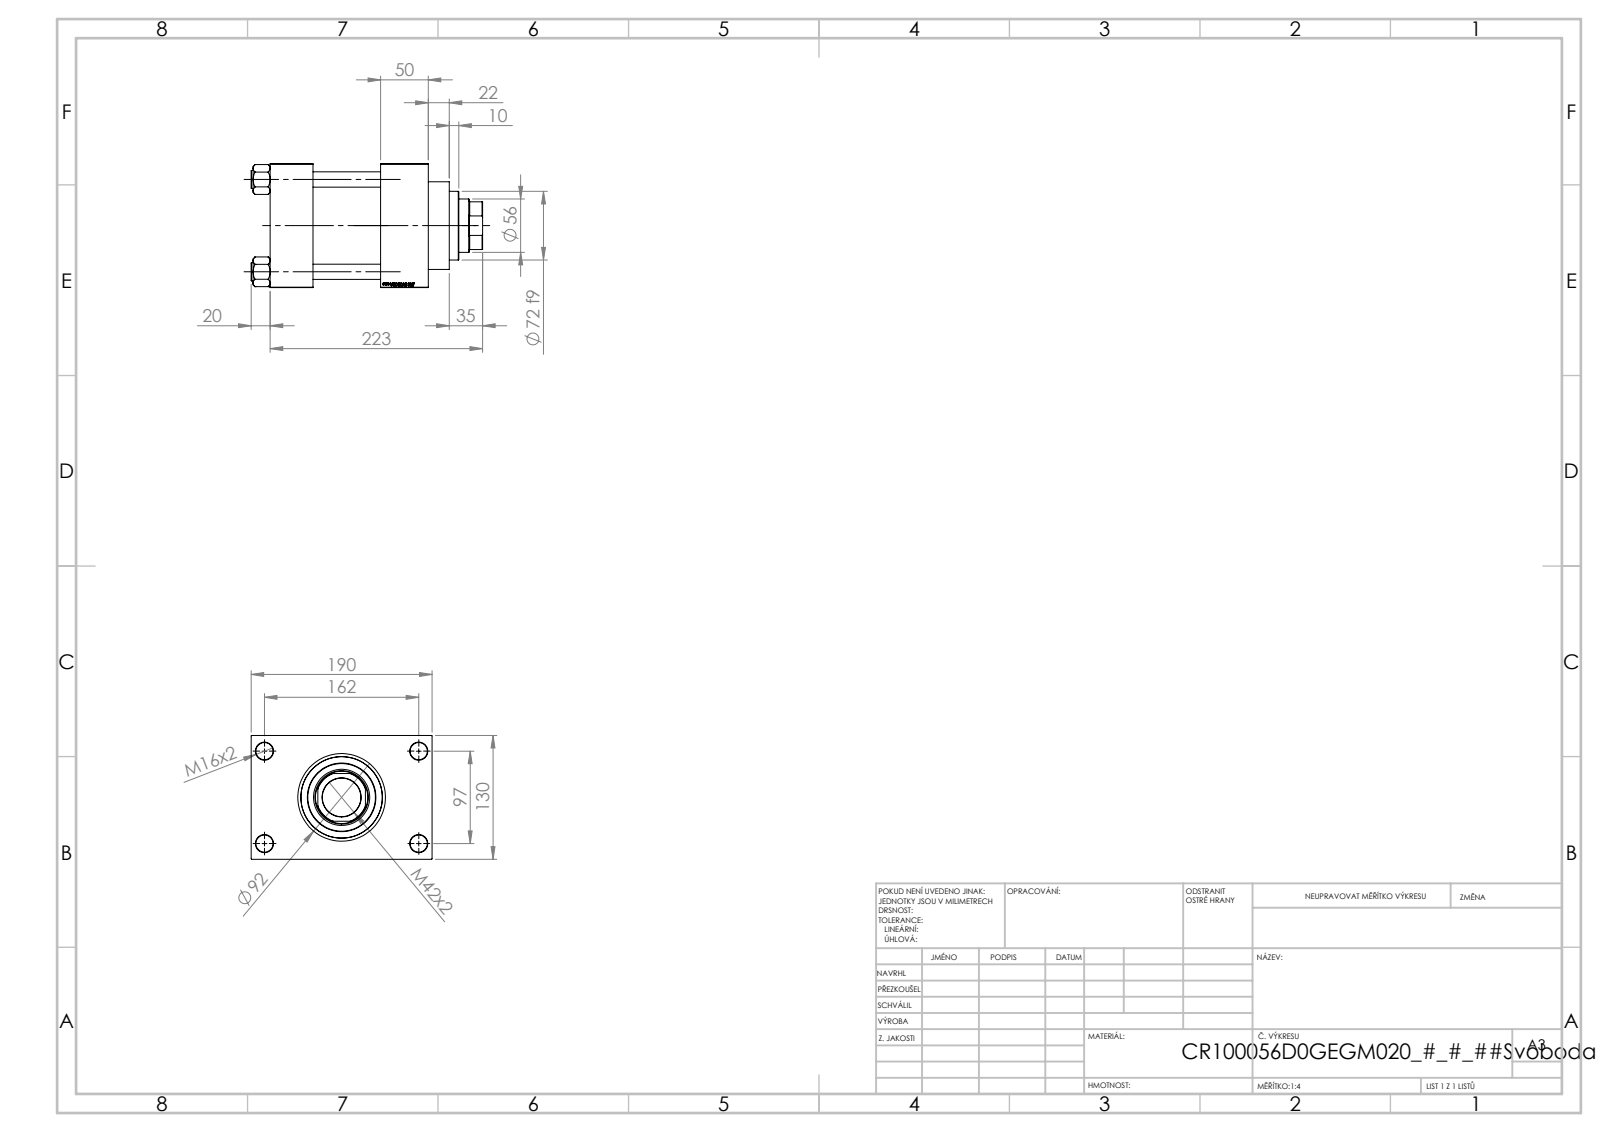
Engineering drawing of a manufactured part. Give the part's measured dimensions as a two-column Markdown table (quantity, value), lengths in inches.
| quantity | value |
| --- | --- |
| part name | V215CR_VCP_D; V215CR_D_TYCINKA; V215CR_D_Body; NUT_M5_D (+1 more) |
| STEP written by | SolidWorks 2019 (CONFIG_CONTROL_DESIGN) |
| units | inches |
| bodies | 11 solids, 1152 faces (545 planar, 89 cylindrical, 518 other) |
| overall size | 9.567 × 7.48 × 5.118 |
| volume | 161.3 in³ |
| surface area | 557.8 in² |
| round holes (diameter × count) | 0.63 × 4, 0.709 × 4, 0.276 × 2, 1.041 × 2, 1.378 × 2, 1.594 × 1, 2.205 × 1, 2.323 × 1, 2.992 × 1, 3.366 × 1, 3.937 × 1 |
| round bosses / shafts (diameter × count) | 0.748 × 4, 4.173 × 1, 3.622 × 1, 2.835 × 1 |
| partial cylindrical surfaces (radius × count) | 1.063 × 1 |
| main face-to-face distances | 5.118, 4.567, 1.969, 1.772, 2.795, 6.535, 4.764, 1.181, 6.299, 7.48 |
| hole center spacings | 1.281, 2.698, 3.717, 3.815, 4.026, 5.096, 6.367, 3.819 |
